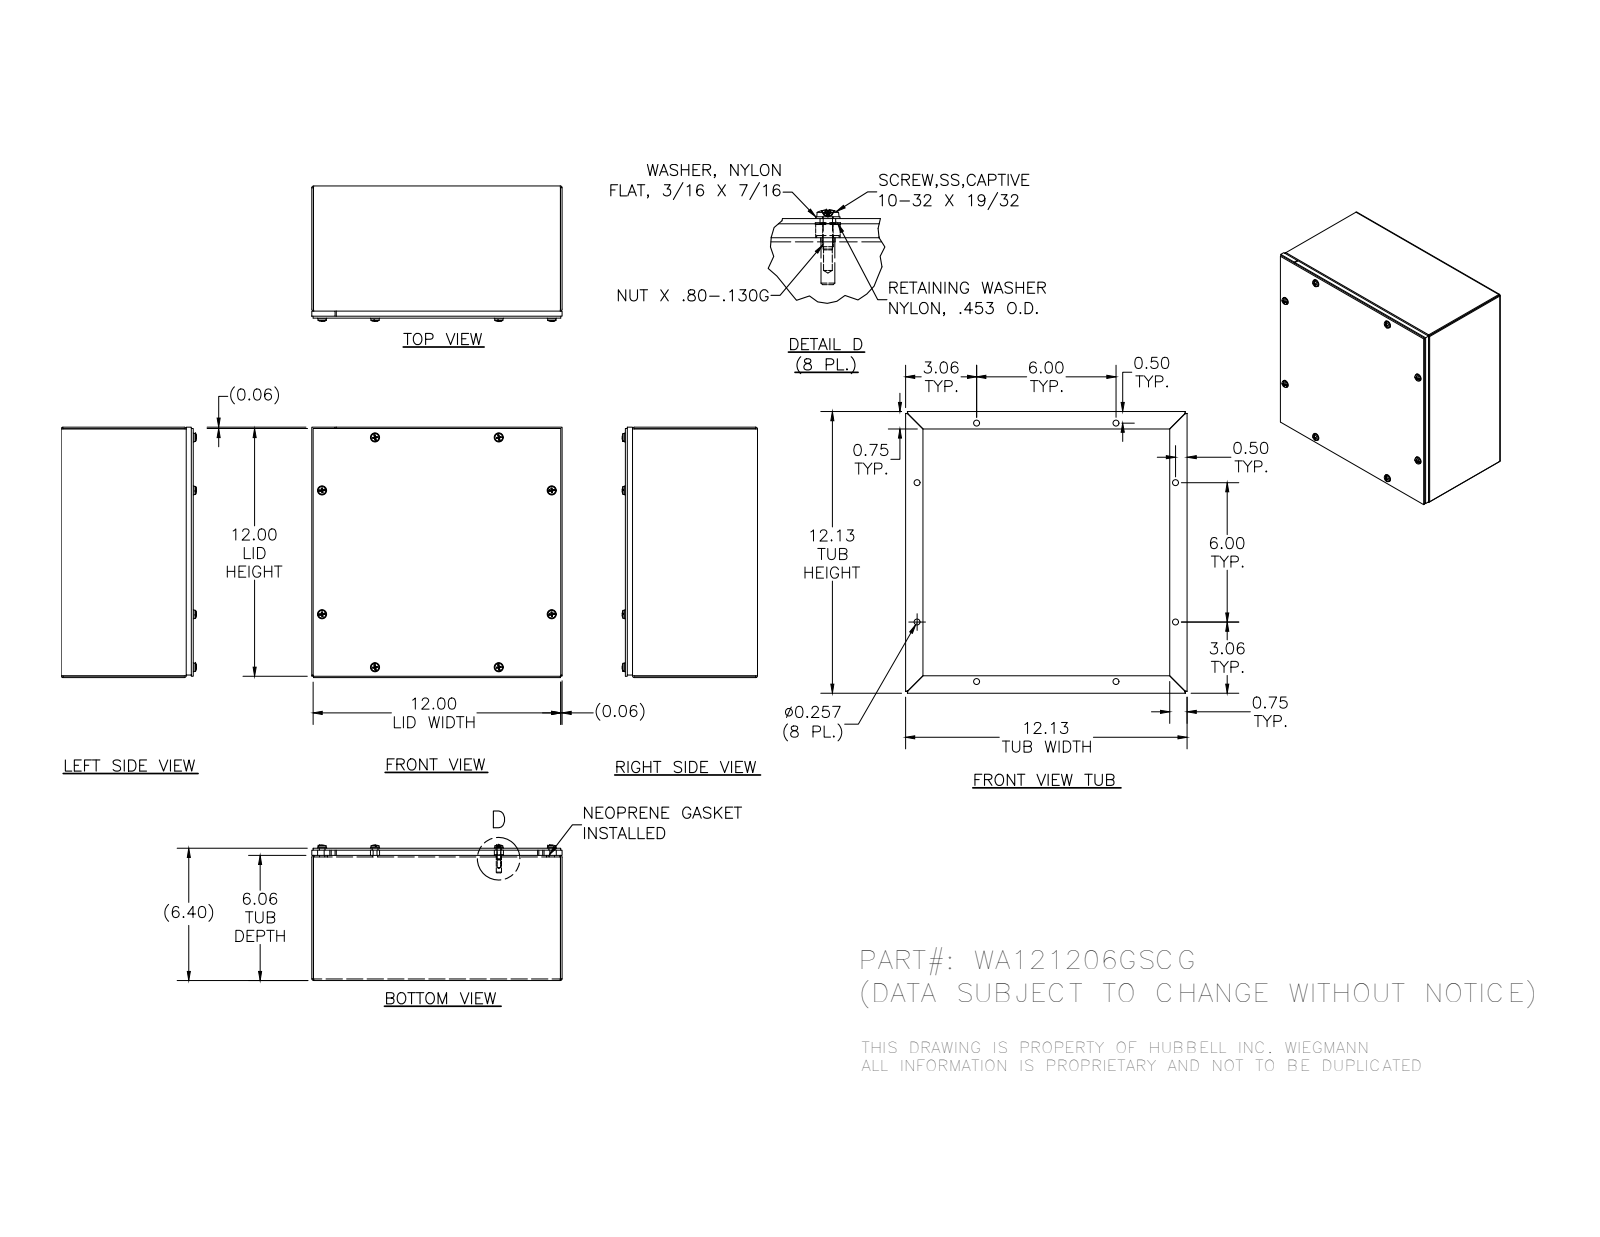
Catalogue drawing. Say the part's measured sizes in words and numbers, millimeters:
The part is named "WA121206GSCGBKP; 39035; 316282; WA1212GSCGLP (+4 more)". Its 3-D file was written by "SolidWorks 2014 (AUTOMOTIVE_DESIGN)". It is 36 solids with 892 faces: 420 planar, 240 cylindrical and 232 other. Overall it measures 308 by 308 by 166.6 millimeters. Its volume is 945 500 cubic millimeters and its surface area 868 400 square millimeters. Round holes: 8 of diameter 4, 8 of diameter 4.8, 8 of diameter 5, 8 of diameter 6.5, 8 of diameter 7.1, 8 of diameter 7.1, 8 of diameter 8. Round bosses or shafts: 8 of diameter 11.5, 8 of diameter 11.1, 8 of diameter 10.3, 8 of diameter 6.3, 8 of diameter 4.2. Partial cylindrical surfaces (rounded edges, fillets, slot ends): 8 of radius 0.4, 8 of radius 2.3, 8 of radius 2.3. The main face-to-face distances are 1.9, 2.4, 306.1, 160.8, 162.7, 158.4, 160.3, 308, 1.9, 306.1. The hole center spacings are 152.4, 227, 92, 307.6, 227, 227, 227, 282.6.
